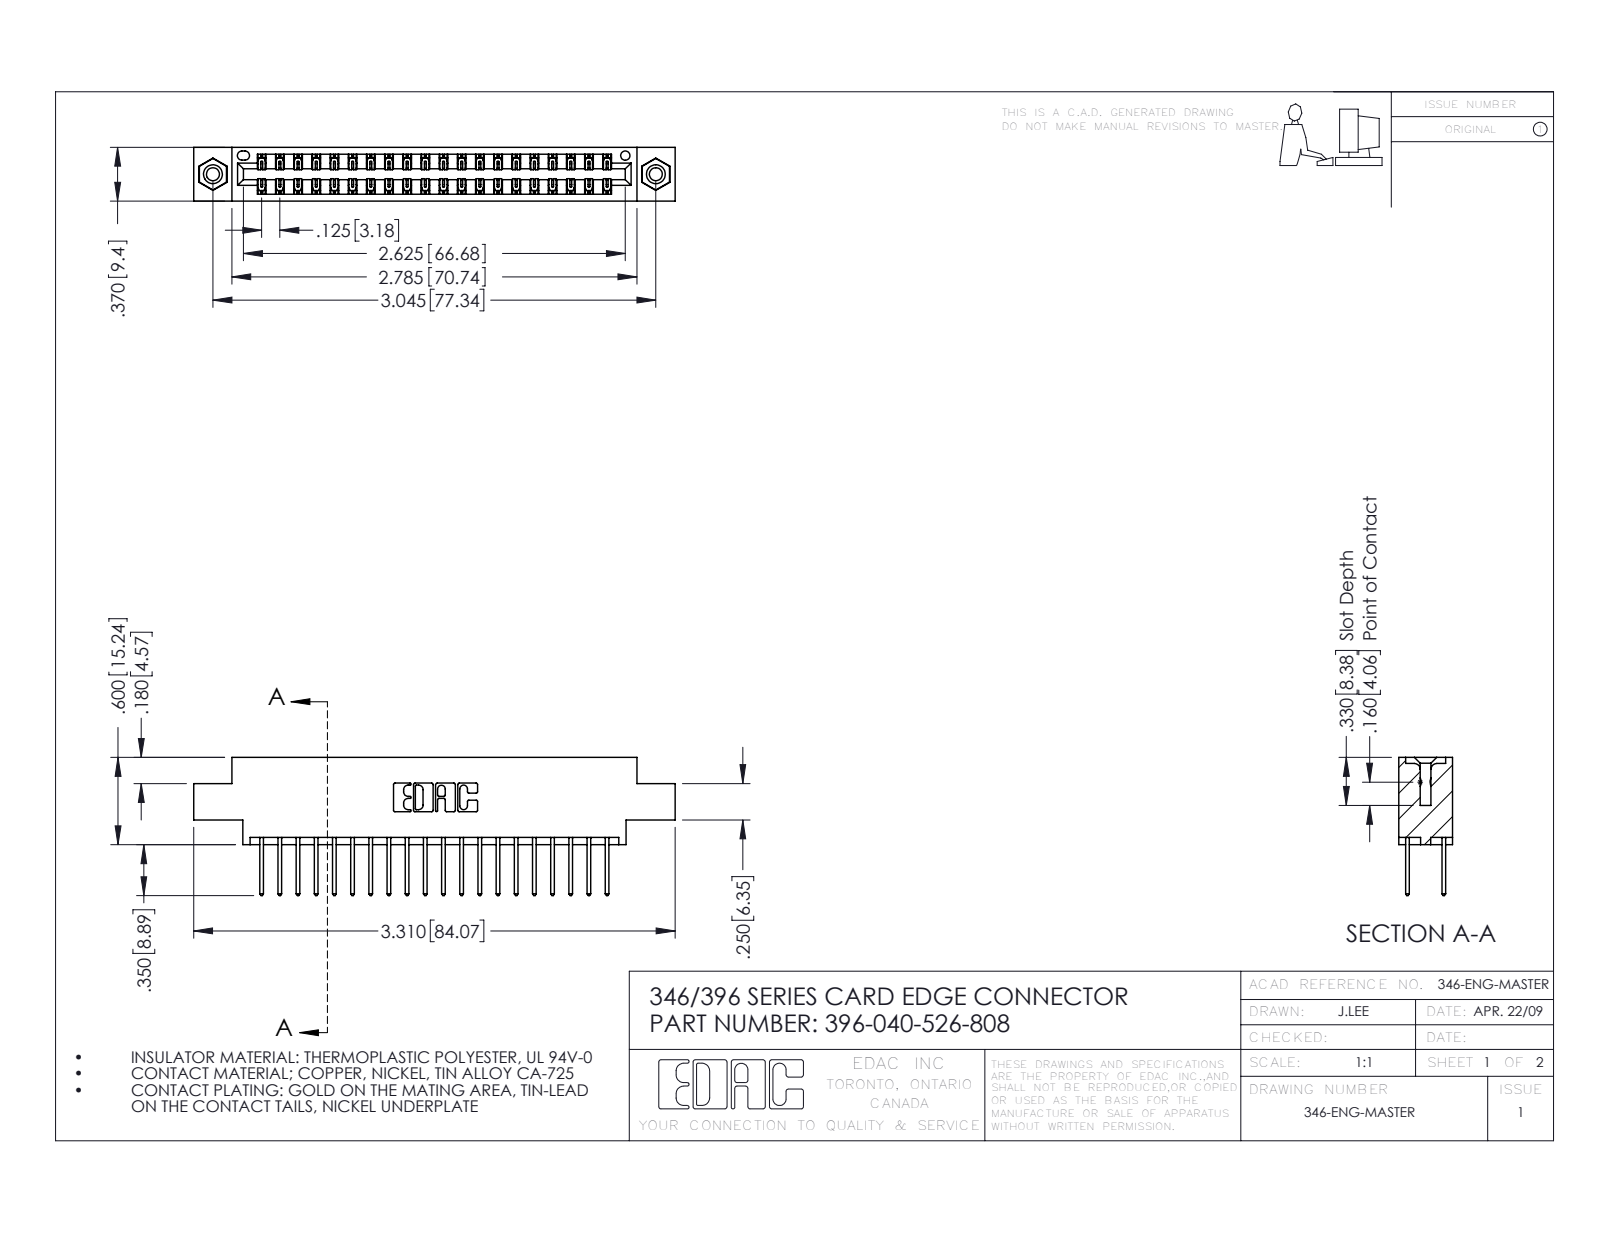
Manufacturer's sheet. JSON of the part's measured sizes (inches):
{"part_name": "396-040-526-808; 345-292-001_345-293-126; 346 Part_0.170 Offset - 0.156 Dia-TI; 345-250-001_345-250-003-102", "step_written_by": "SolidWorks 2016 (CONFIG_CONTROL_DESIGN)", "units": "inches", "bodies": {"solids": 43, "faces": 2266, "planar": 1512, "cylindrical": 738, "other": 16}, "overall_size": [3.31, 0.95, 0.37], "volume_in3": 0.484, "surface_area_in2": 17.13, "round_holes": [[0.089, 2], [0.125, 2], [0.156, 2], [0.064, 1]], "round_bosses_or_shafts": [[0.155, 2]], "partial_cylinders_radius": [[0.006, 60], [0.01, 40], [0.01, 22], [0.007, 6], [0.031, 6], [0.026, 3], [0.014, 2], [0.022, 2]], "face_to_face_distances": [0.048, 0.322, 0.25, 0.37, 0.072, 0.298, 0.025, 0.275, 0.222, 0.148], "hole_center_spacings": [0.246, 2.837, 3.045]}
